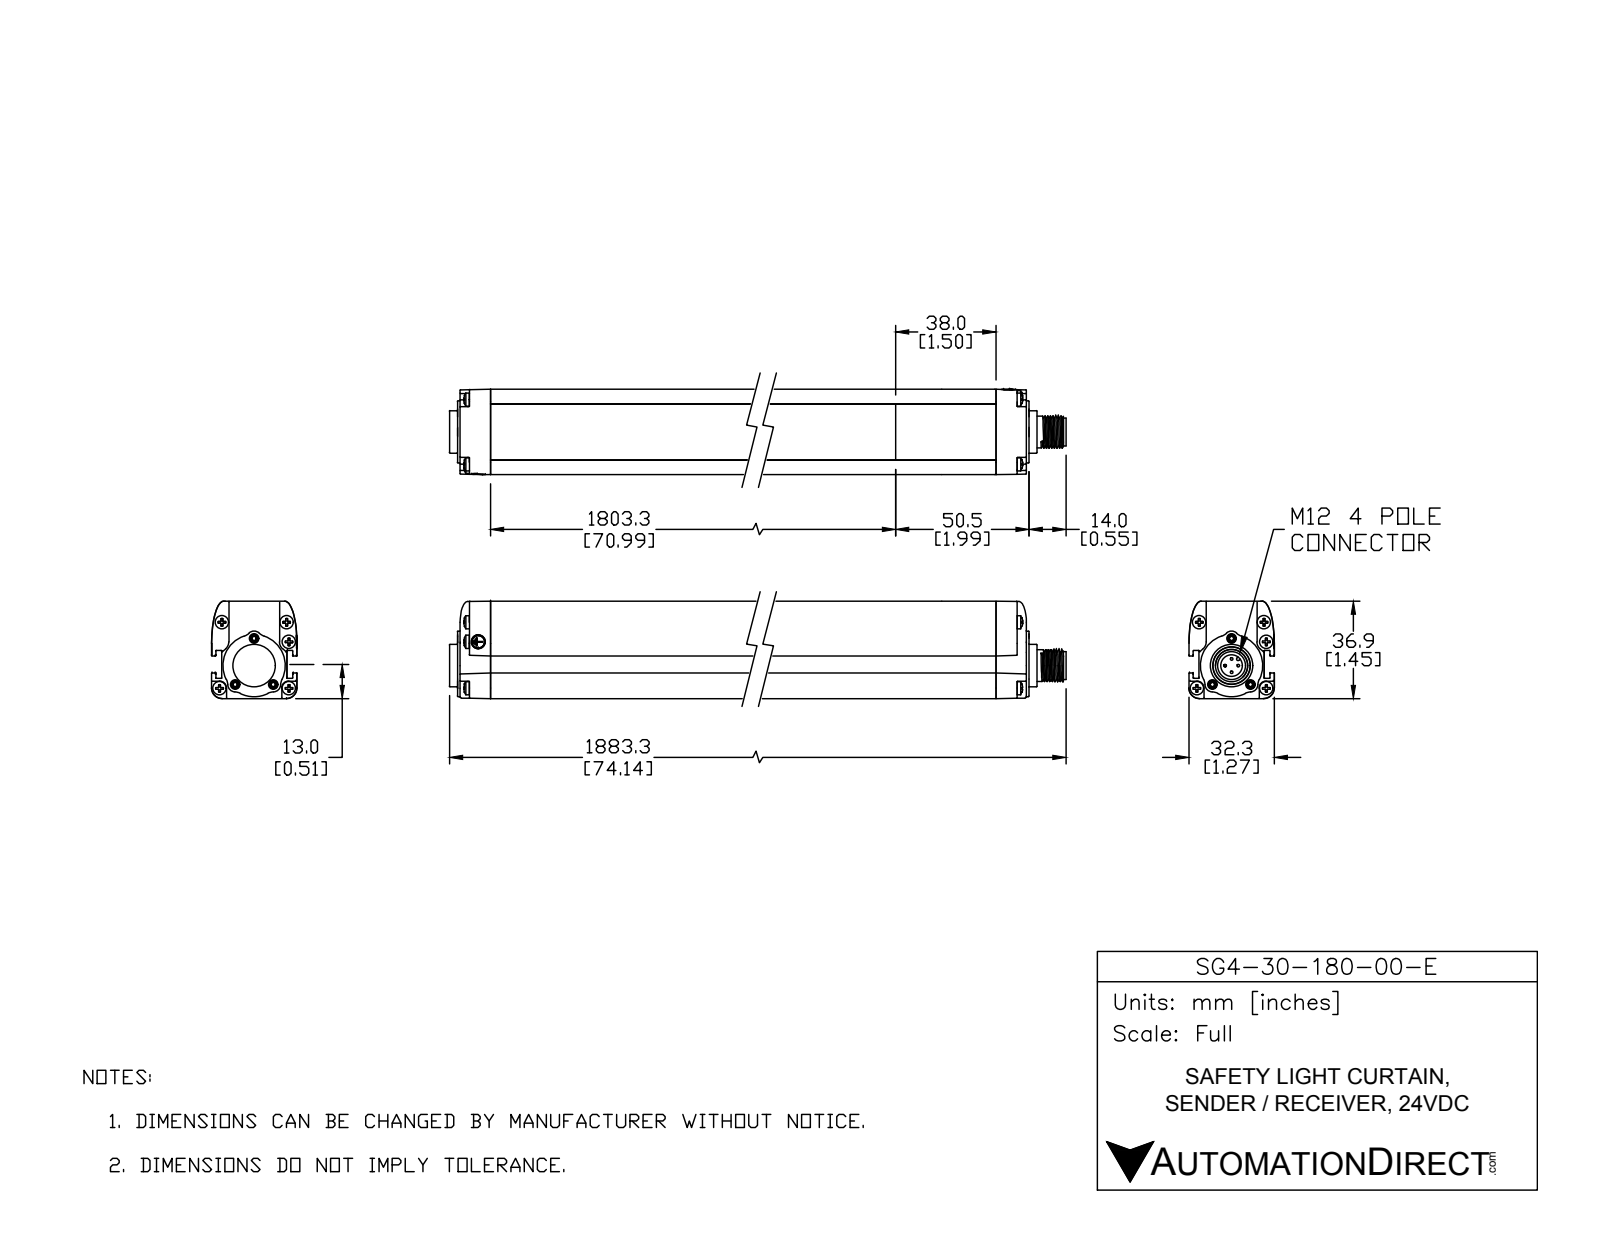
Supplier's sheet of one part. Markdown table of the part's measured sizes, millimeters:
| quantity | value |
| --- | --- |
| part name | SG4-30-180-OO-E |
| STEP written by | SolidWorks 2017 (AUTOMOTIVE_DESIGN) |
| units | millimeters |
| bodies | 29 solids, 1674 faces (410 planar, 591 cylindrical, 673 other) |
| overall size | 1883.3 × 63 × 52.2 |
| volume | 1 940 000 mm³ |
| surface area | 450 500 mm² |
| round holes (diameter × count) | 2.7 × 6, 5.3 × 6, 2.1 × 4, 4.2 × 4, 6.6 × 4, 1.5 × 3, 3.6 × 3, 8.2 × 1, 9.6 × 1, 11 × 1, 14.3 × 1 |
| round bosses / shafts (diameter × count) | 5 × 10, 10 × 4, 1 × 4, 4.7 × 2, 16 × 1, 14 × 1, 12 × 1, 10.5 × 1 |
| partial cylindrical surfaces (radius × count) | 0.2 × 148, 0.1 × 120, 0.2 × 18, 2.7 × 18, 3 × 8, 5 × 7, 2.8 × 3, 0.4 × 2 |
| main face-to-face distances | 2, 32.3, 36.3, 3.8, 28.5, 34.3, 4, 24.7, 8.5, 1.6 |
| hole center spacings | 14.5, 1801.3, 10.2, 6.1, 7.4, 13.2, 13.7, 15.7 |
